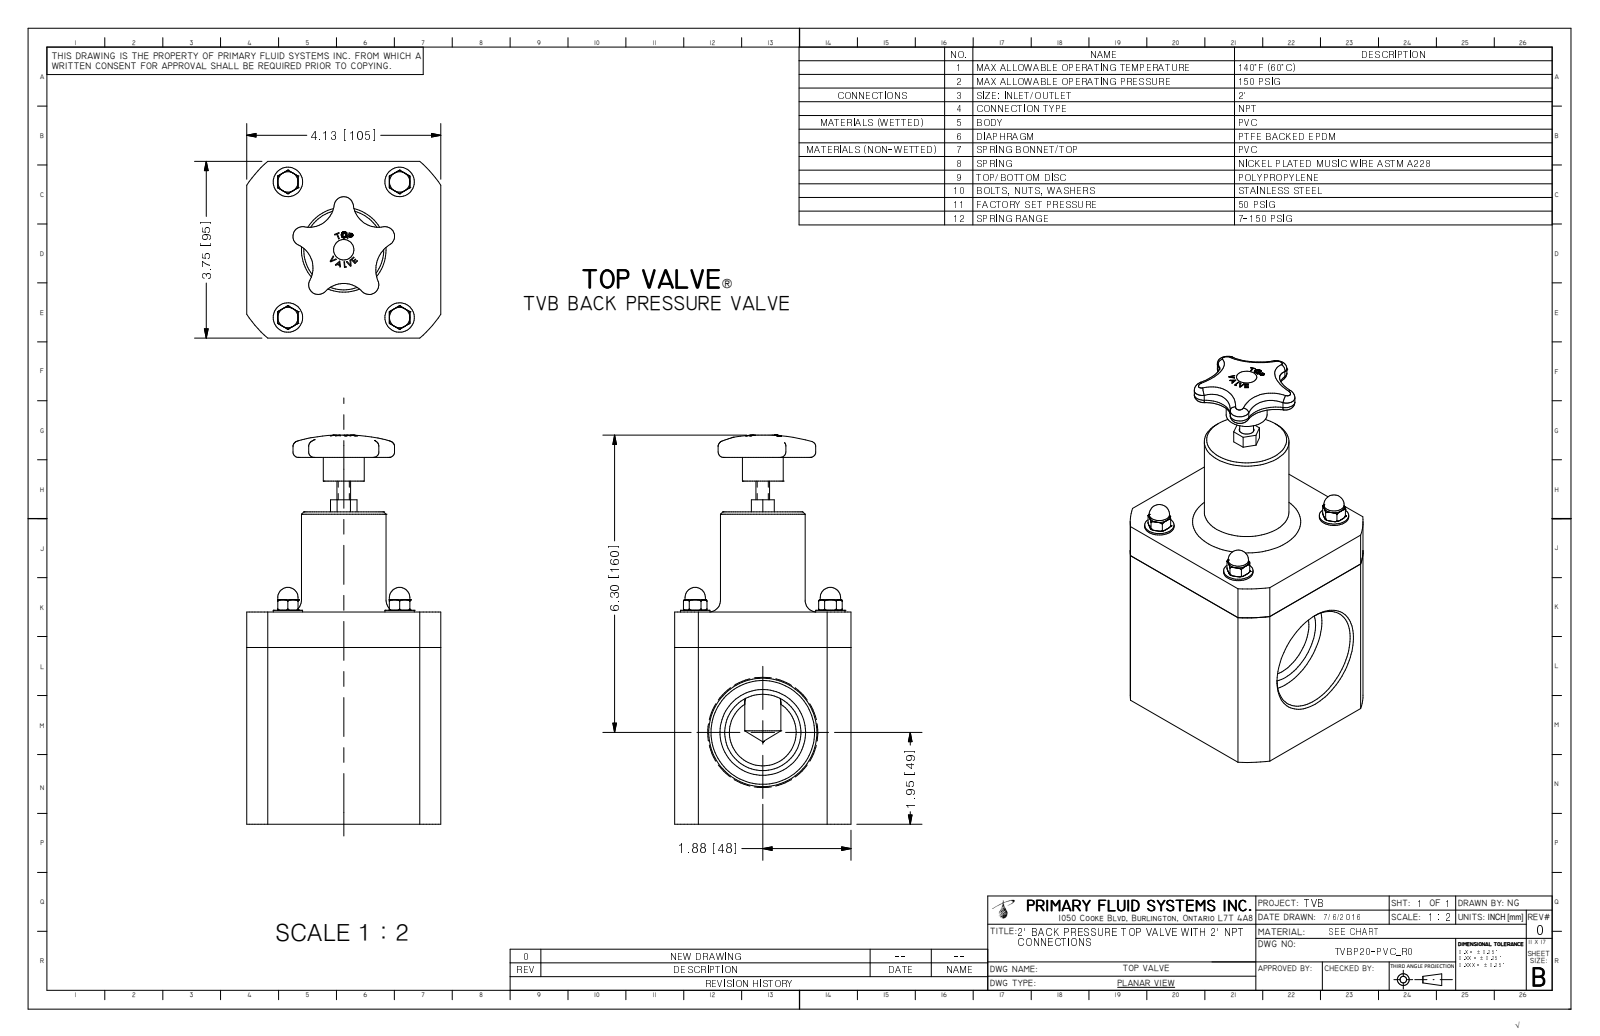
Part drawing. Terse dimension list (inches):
name: TVBP20-PVC_R0
written by: Autodesk Inventor 2009 (AUTOMOTIVE_DESIGN)
unit: in
bodies: 1 solid, 337 faces (144 planar, 45 cylindrical, 148 other)
size: 8.252 × 4.125 × 3.75
volume: 67.84 in³; area: 135.6 in²
holes: 4× ⌀0.175, 1× ⌀2.2
bosses: 4× ⌀0.625, 4× ⌀0.433, 4× ⌀0.375, 1× ⌀1.8, 1× ⌀0.87, 1× ⌀0.293
rounds: 5× R0.085, 5× R0.205, 4× R0.536, 4× R0.656, 1× R0.625, 1× R0.745, 1× R2.475
face distances: 3.75, 4.5, 4.125, 0.9, 3.225, 2.325, 6.625, 2.125, 0.433, 4.536
hole spacings: 2.375, 2.875, 3.729
